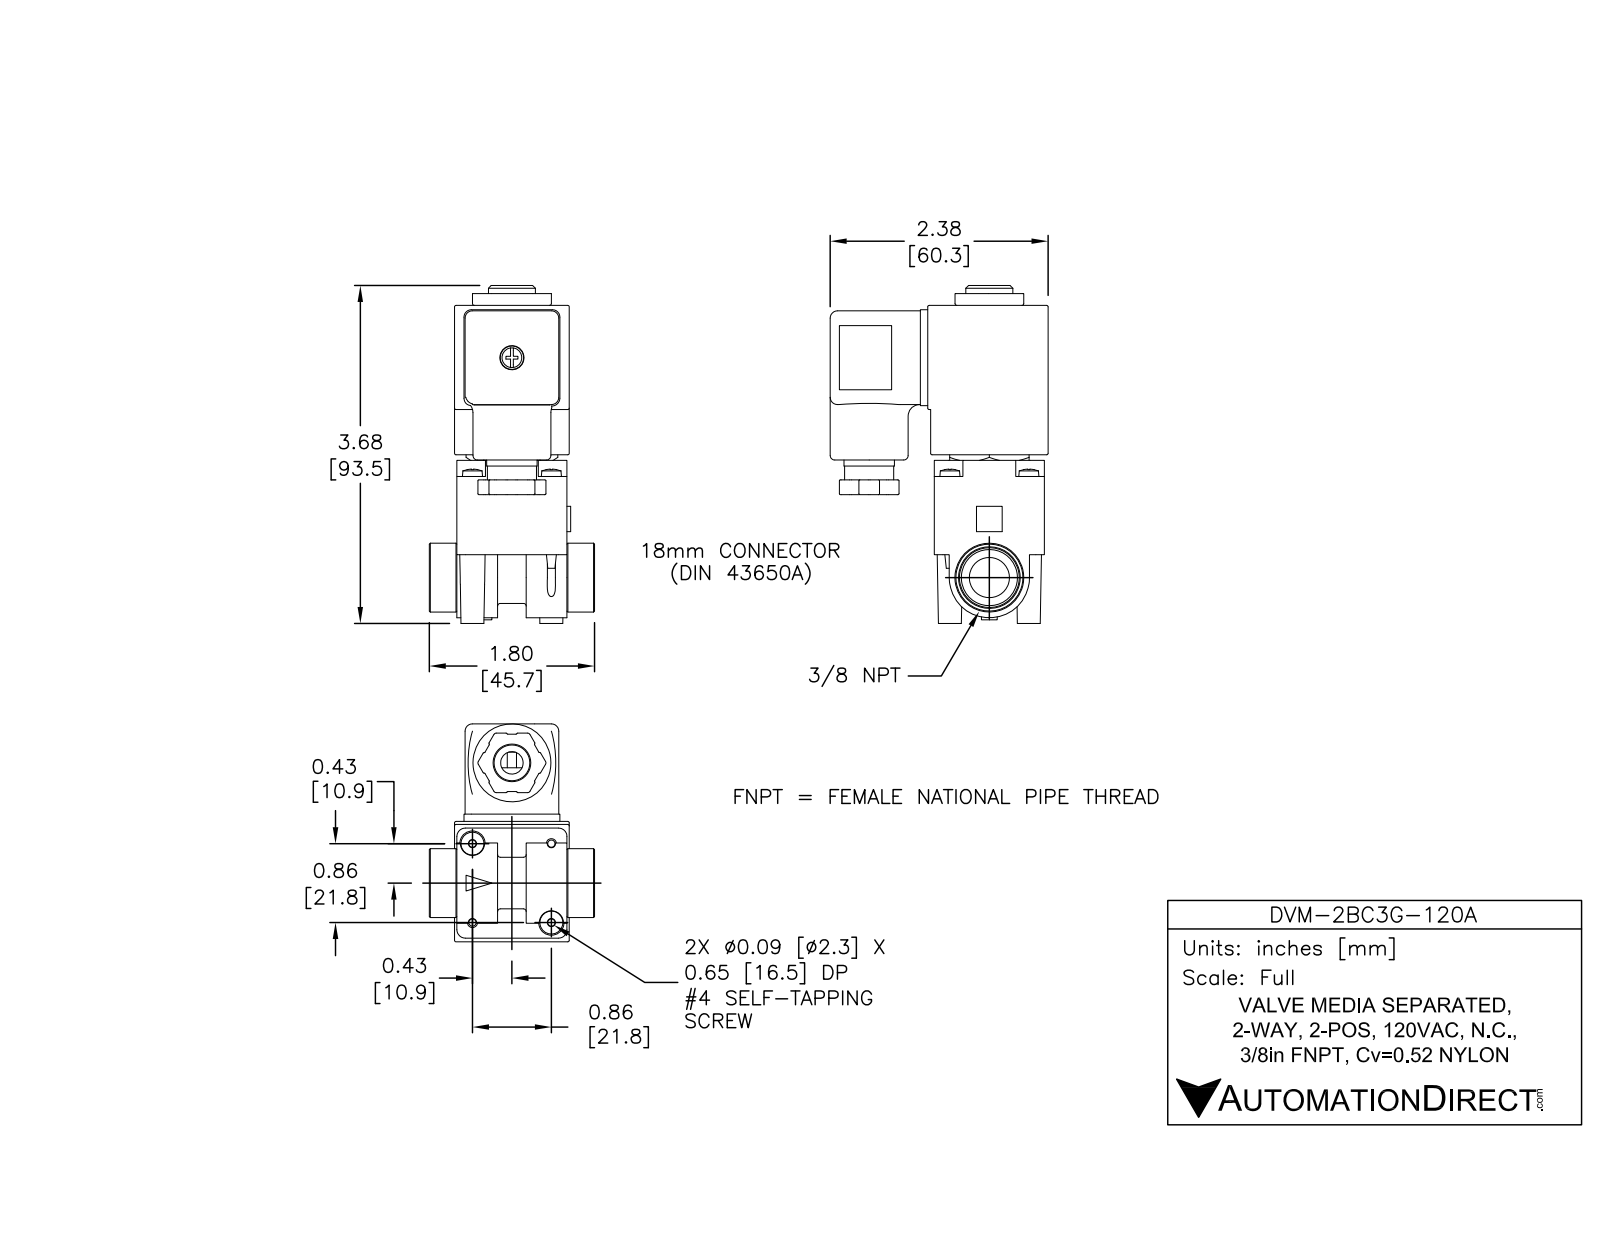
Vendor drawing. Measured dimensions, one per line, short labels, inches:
name: DVM-2BC3G-120A
written by: SolidWorks 2015 (AUTOMOTIVE_DESIGN)
unit: in
bodies: 14 solids, 1775 faces (895 planar, 351 cylindrical, 529 other)
size: 3.683 × 2.375 × 1.8
volume: 5.115 in³; area: 68.03 in²
holes: 4× ⌀0.112, 2× ⌀0.06, 2× ⌀0.089, 2× ⌀0.315, 1× ⌀0.12, 1× ⌀0.157, 1× ⌀0.203, 1× ⌀0.245, 1× ⌀0.25, 1× ⌀0.263, 1× ⌀0.39, 1× ⌀0.4
bosses: 4× ⌀0.217, 4× ⌀0.125, 1× ⌀0.875, 1× ⌀0.875, 1× ⌀0.85, 1× ⌀0.807, 1× ⌀0.68, 1× ⌀0.535
rounds: 54× R0.01, 21× R0.005, 17× R0.016, 12× R0.02, 12× R0.03, 12× R0.031, 12× R0.08, 8× R0.05
face distances: 1.25, 1.2, 0.163, 1.087, 0.048, 0.137, 0.974, 1.225, 0.963, 0.04
hole spacings: 0.608, 0.608, 0.684, 0.86, 0.86, 0.98, 1.216, 1.457
